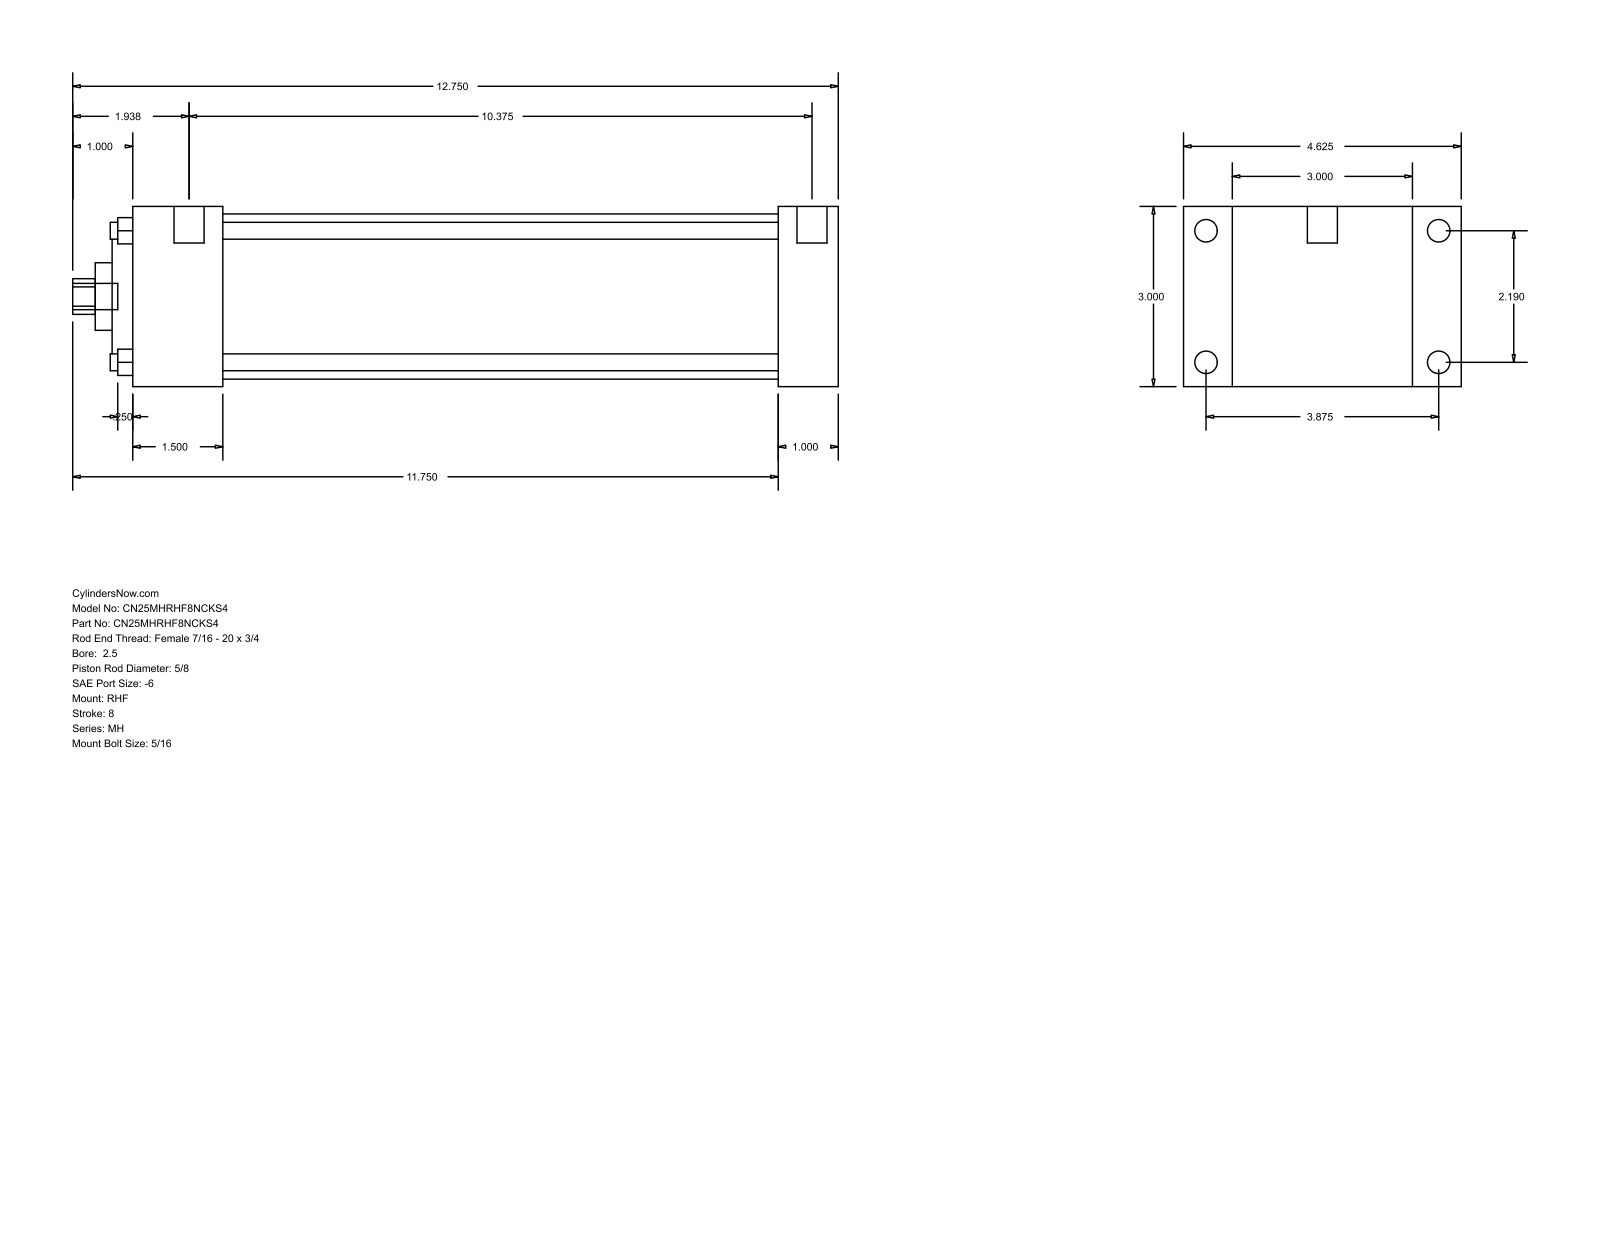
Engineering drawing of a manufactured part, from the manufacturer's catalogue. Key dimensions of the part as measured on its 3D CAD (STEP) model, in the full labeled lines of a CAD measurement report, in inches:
Part name (STEP PRODUCT): MH_RHF__0250_0.625
STEP written by: GSSL Pune (CONFIG_CONTROL_DESIGN)
Units: inches
Bodies: 0 solids, 90 faces (61 planar, 29 cylindrical, 0 other)
Overall size (bounding box): 12.75 × 4.625 × 3
Round holes (diameter × count): ⌀0.281 ×4, ⌀0.625 ×1, ⌀1.125 ×1, ⌀2.187 ×1, ⌀2.75 ×1
Round bosses / shafts (diameter × count): ⌀0.375 ×4, ⌀0.219 ×4, ⌀0.5 ×2, ⌀0.437 ×1
Partial cylindrical surfaces — rounded edges, fillets, slot ends (radius × count): R0.297 ×1
Main face-to-face distances: 3, 1, 0.813, 3.813, 11.75, 10.75, 4.625, 1.5, 9.25, 10.25
Hole centre spacings: 1.548, 2.19, 3.097
